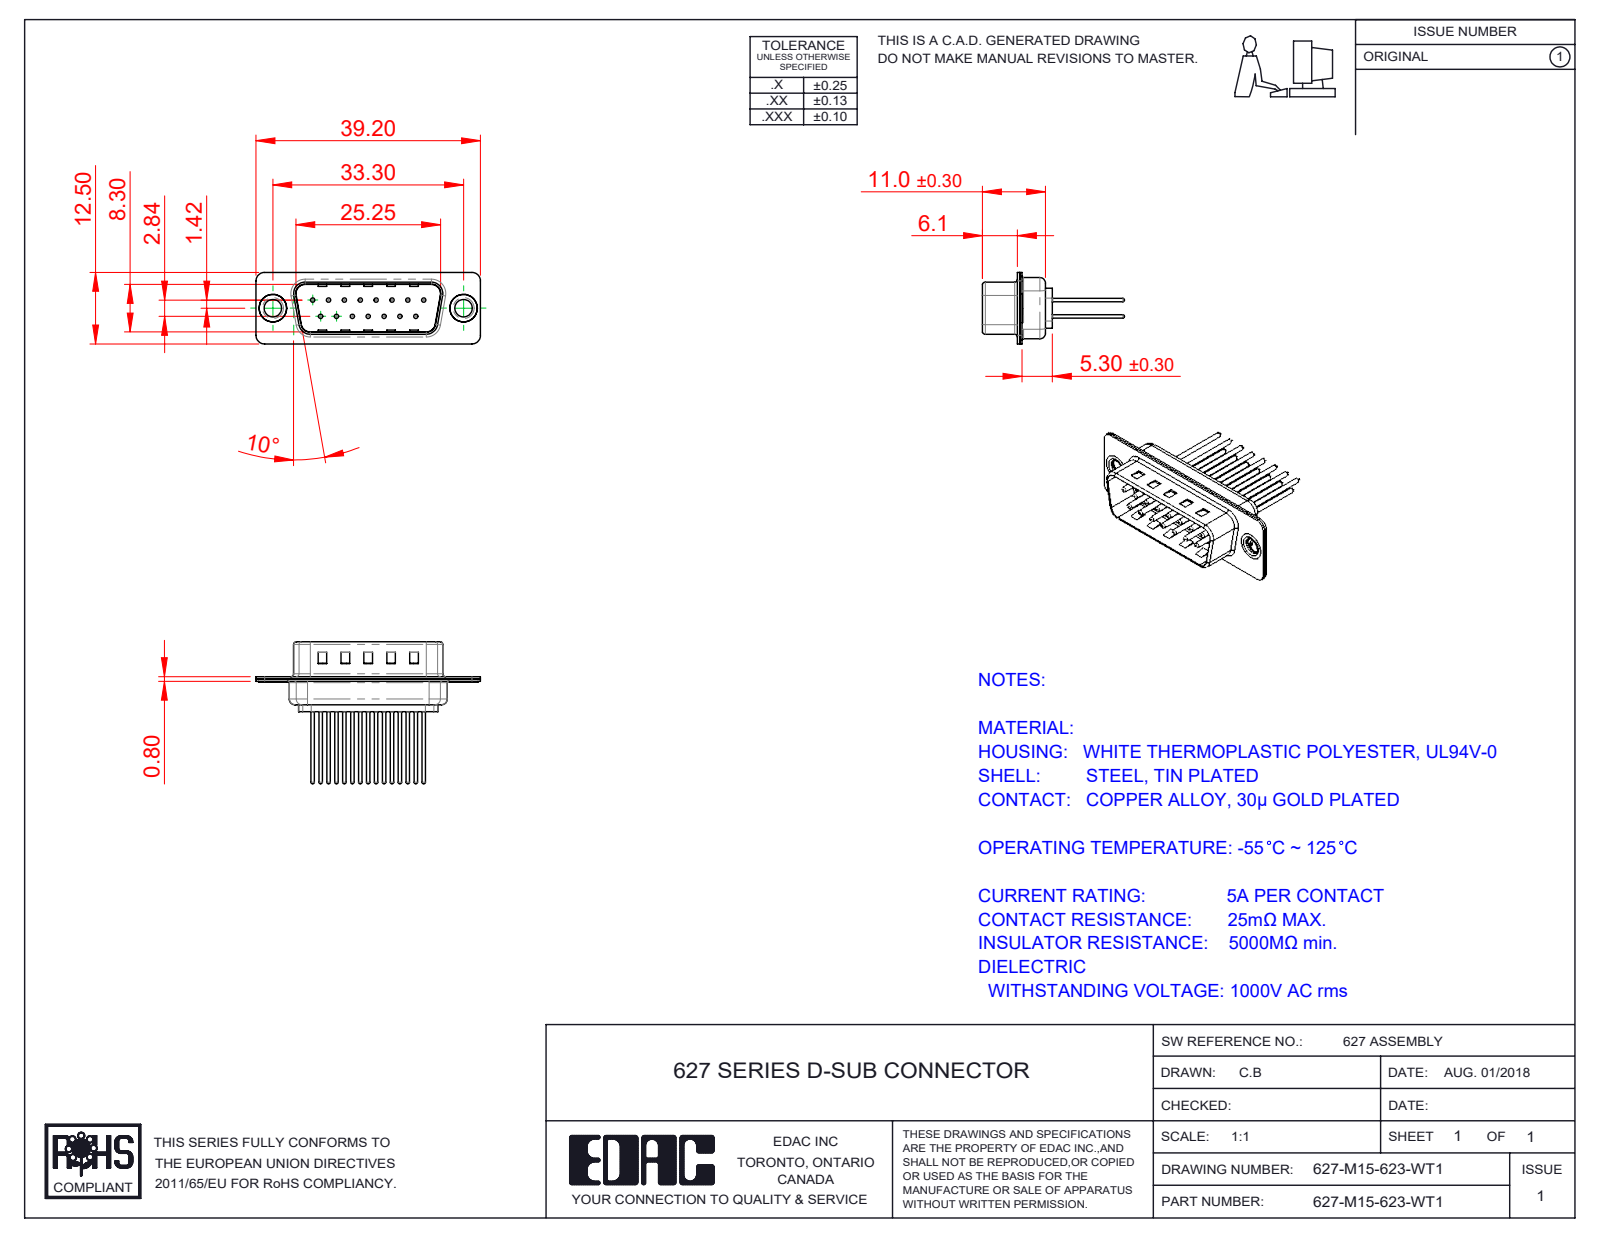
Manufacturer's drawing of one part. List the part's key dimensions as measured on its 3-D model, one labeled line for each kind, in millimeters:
Part name (STEP PRODUCT): 627M Shell Front_15 Contacts; 627M Contact Row 1_23; 627-M15-623-WT1; 627M Thru Hole Rivet (+3 more)
STEP written by: SolidWorks 2020 (CONFIG_CONTROL_DESIGN)
Units: millimetres
Bodies: 20 solids, 869 faces (244 planar, 327 cylindrical, 298 other)
Overall size (bounding box): 39.2 × 24.77 × 12.5
Volume: 1 794 mm³ · Surface area: 4 857 mm²
Round holes (diameter × count): ⌀0.75 ×15, ⌀1.6 ×15, ⌀2 ×15, ⌀3.05 ×2, ⌀4 ×2, ⌀4.8 ×2
Round bosses / shafts (diameter × count): ⌀1.5 ×15, ⌀0.6 ×15, ⌀5 ×2, ⌀4.9 ×2, ⌀3.55 ×2
Partial cylindrical surfaces — rounded edges, fillets, slot ends (radius × count): R1.5 ×16, R2 ×12, R0.5 ×8, R1.6 ×8, R0.25 ×4, R0.6 ×4, R0.65 ×4, R0.9 ×4
Main face-to-face distances: 0.4, 0.8, 9.5, 9.1, 8.7, 9.9, 1.2, 6.1, 5.3, 5.7
Hole centre spacings: 3.16, 2.77, 5.54, 8.31, 11.08, 5.03, 5.04, 7.48
